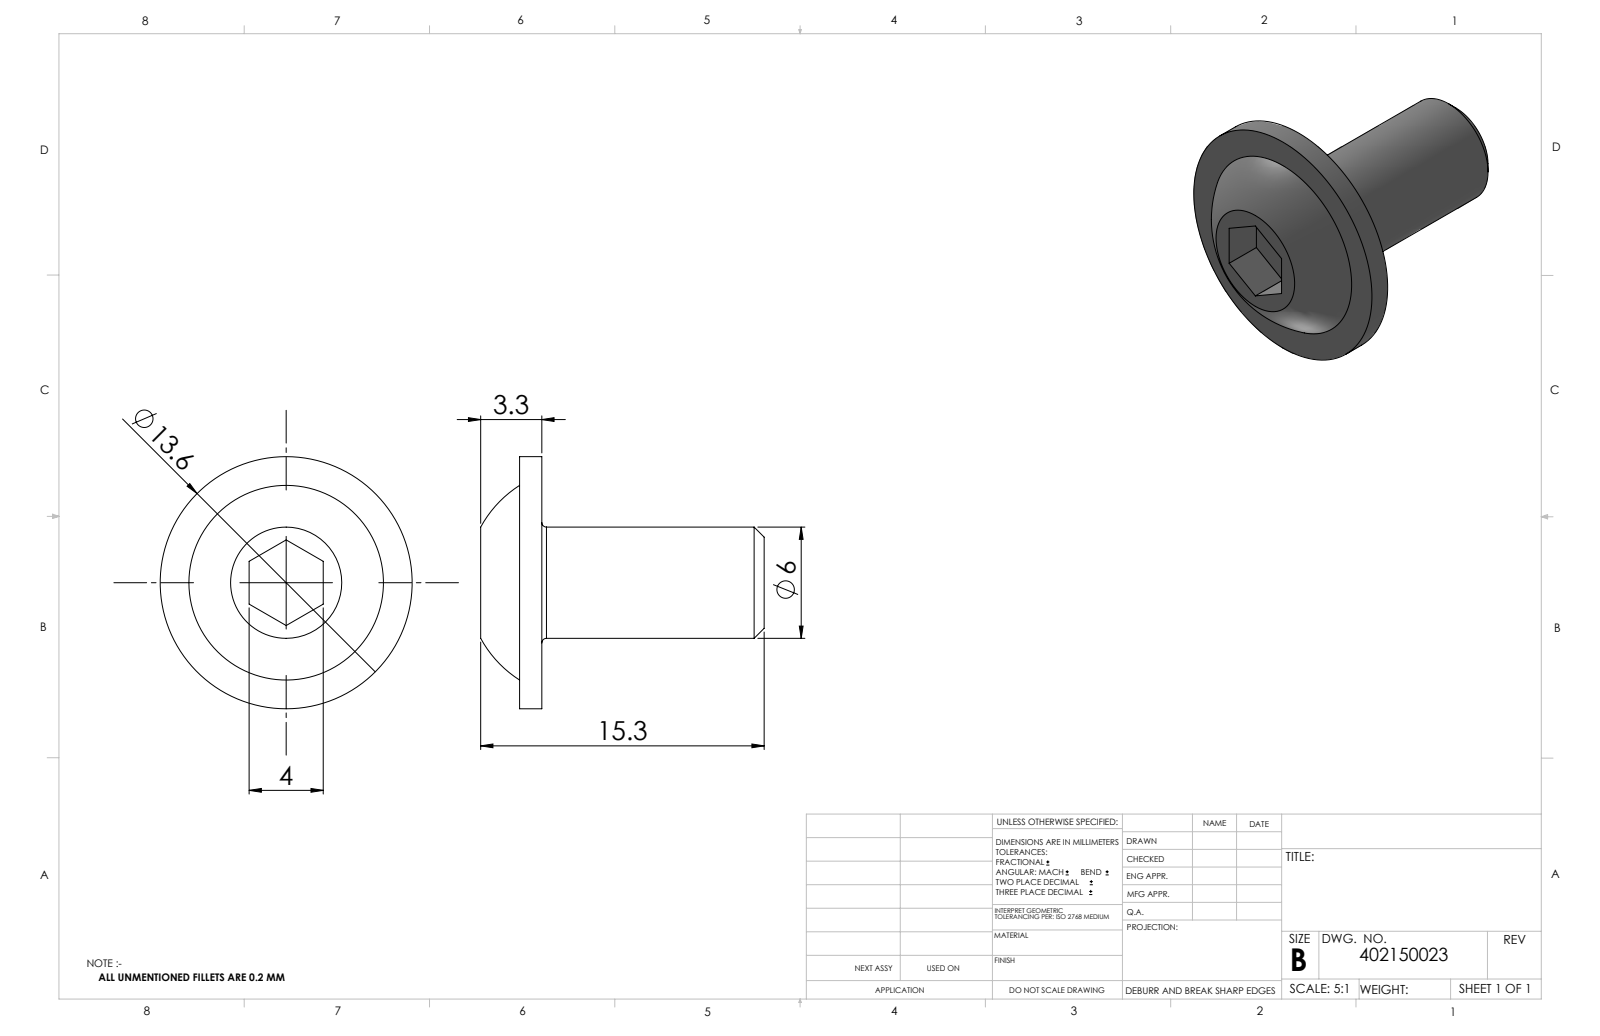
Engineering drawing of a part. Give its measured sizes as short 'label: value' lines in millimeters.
name: 402150023_c_1
written by: SolidWorks 2014 (CONFIG_CONTROL_DESIGN)
unit: mm
bodies: 1 solid, 21 faces (11 planar, 4 cylindrical, 6 other)
size: 15.3 × 13.6 × 13.6
volume: 608 mm³; area: 612 mm²
bosses: 1× ⌀13.6, 1× ⌀6
face distances: 1.2, 12, 13.2, 15.3, 3.3, 2.1, 4, 13.22, 1.22, 2.08
